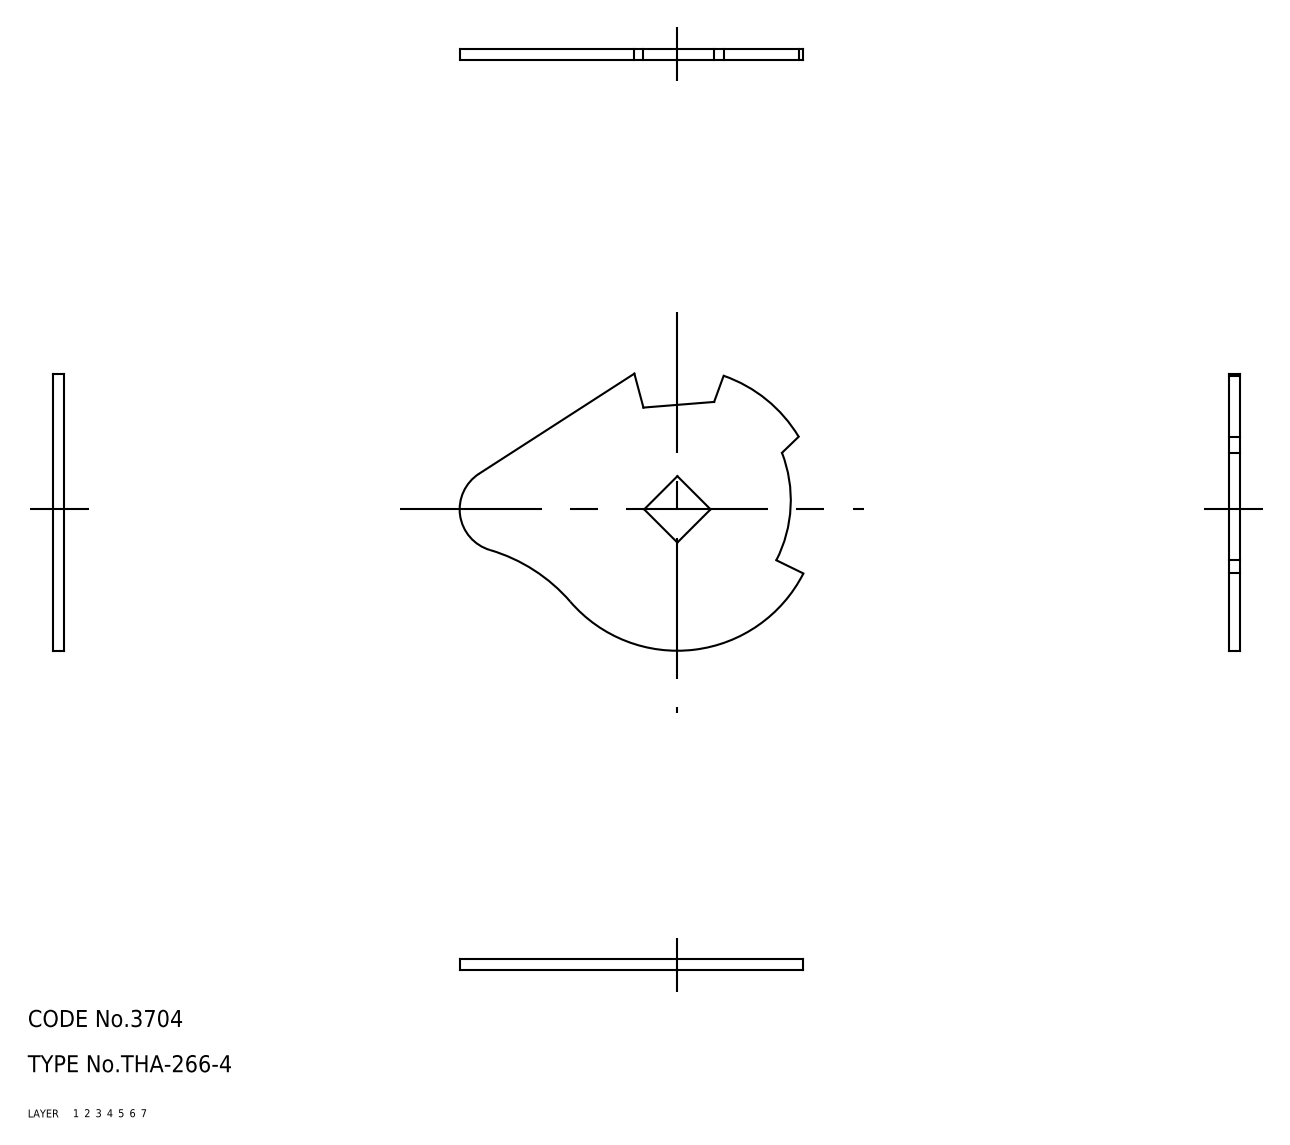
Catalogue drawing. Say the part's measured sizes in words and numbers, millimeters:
The part is named "cam". Its 3-D file was written by "CADfix (AUTOMOTIVE_DESIGN)". It is 1 solid with 17 faces: 0 planar, 0 cylindrical and 17 other. Overall it measures 60.78 by 49 by 2 millimeters. Its volume is 3 881 cubic millimeters and its surface area 4 319 square millimeters.
